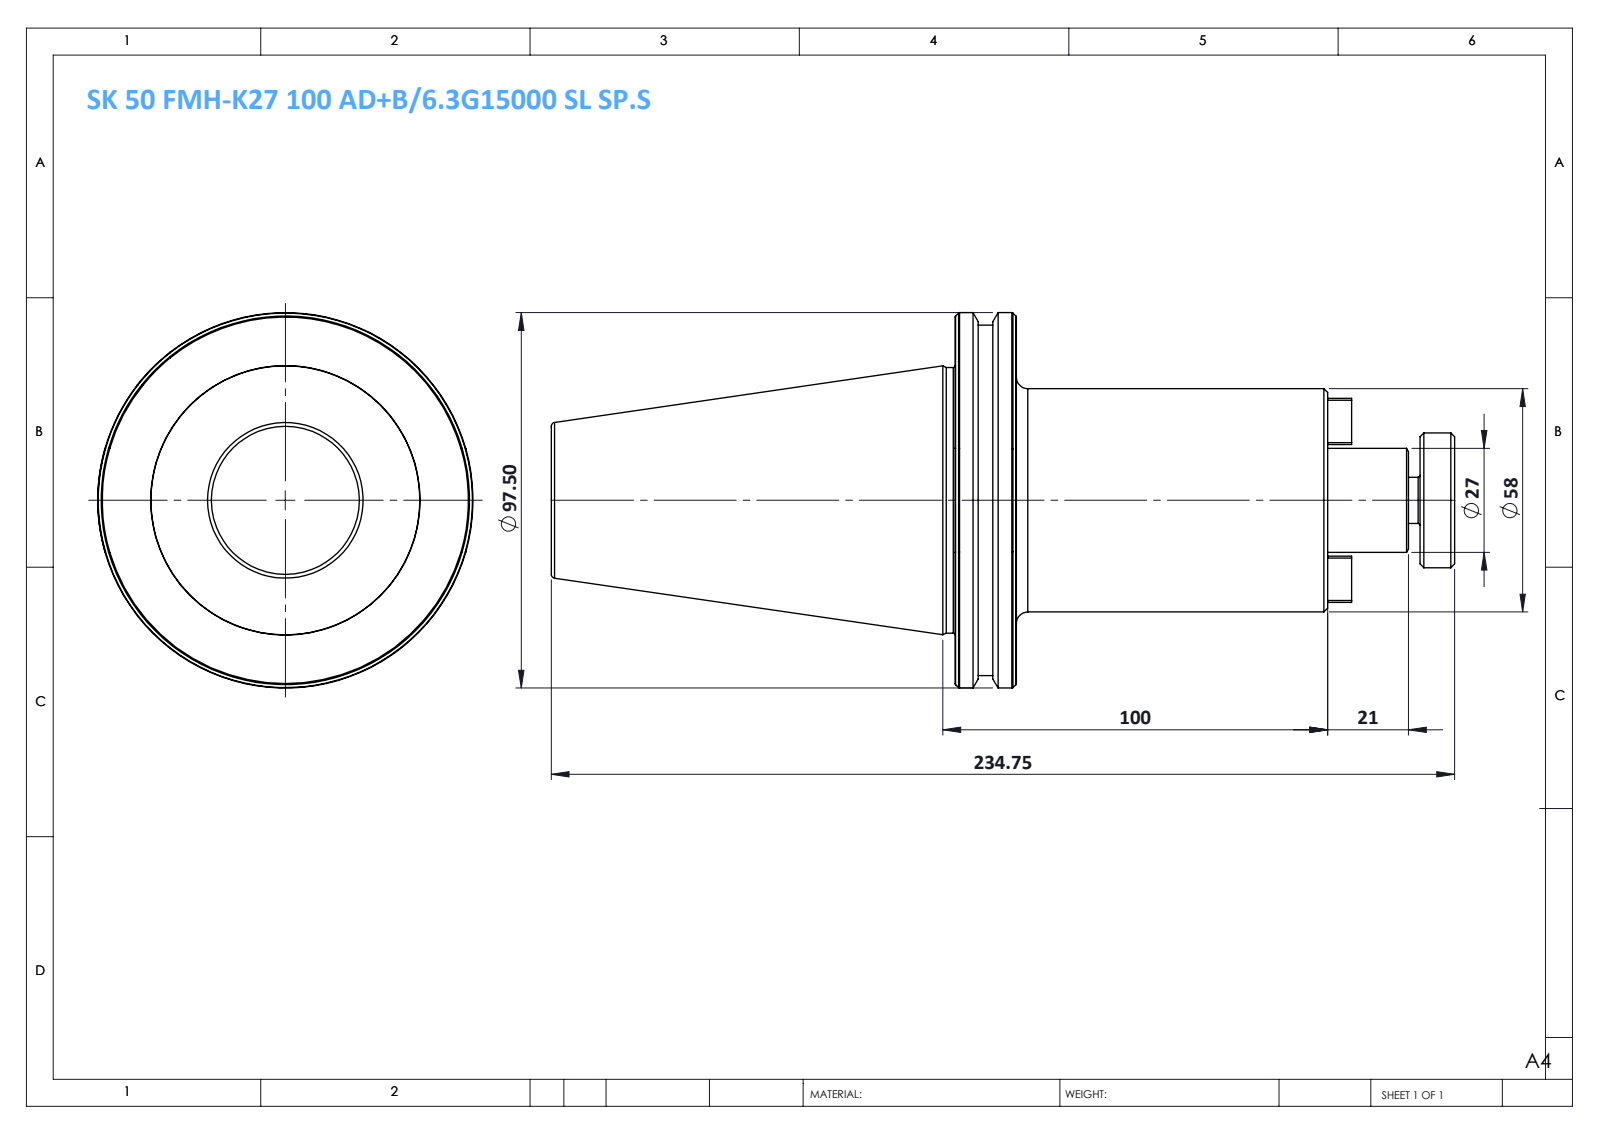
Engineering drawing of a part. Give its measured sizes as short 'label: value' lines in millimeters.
name: SK50 FMH27 100 AD-6.3G15000 SL SP.S
written by: SolidWorks 2014 (CONFIG_CONTROL_DESIGN)
unit: mm
bodies: 1 solid, 99 faces (27 planar, 16 cylindrical, 56 other)
size: 234.75 × 97.5 × 97.5
volume: 610 228 mm³; area: 55 987 mm²
bosses: 1× ⌀97.5, 1× ⌀91, 1× ⌀69, 1× ⌀58, 1× ⌀35, 1× ⌀27, 1× ⌀12
face distances: 15.9, 80.9, 96.8, 201.75, 120.85, 104.95, 33, 113.9, 129.8, 234.75
